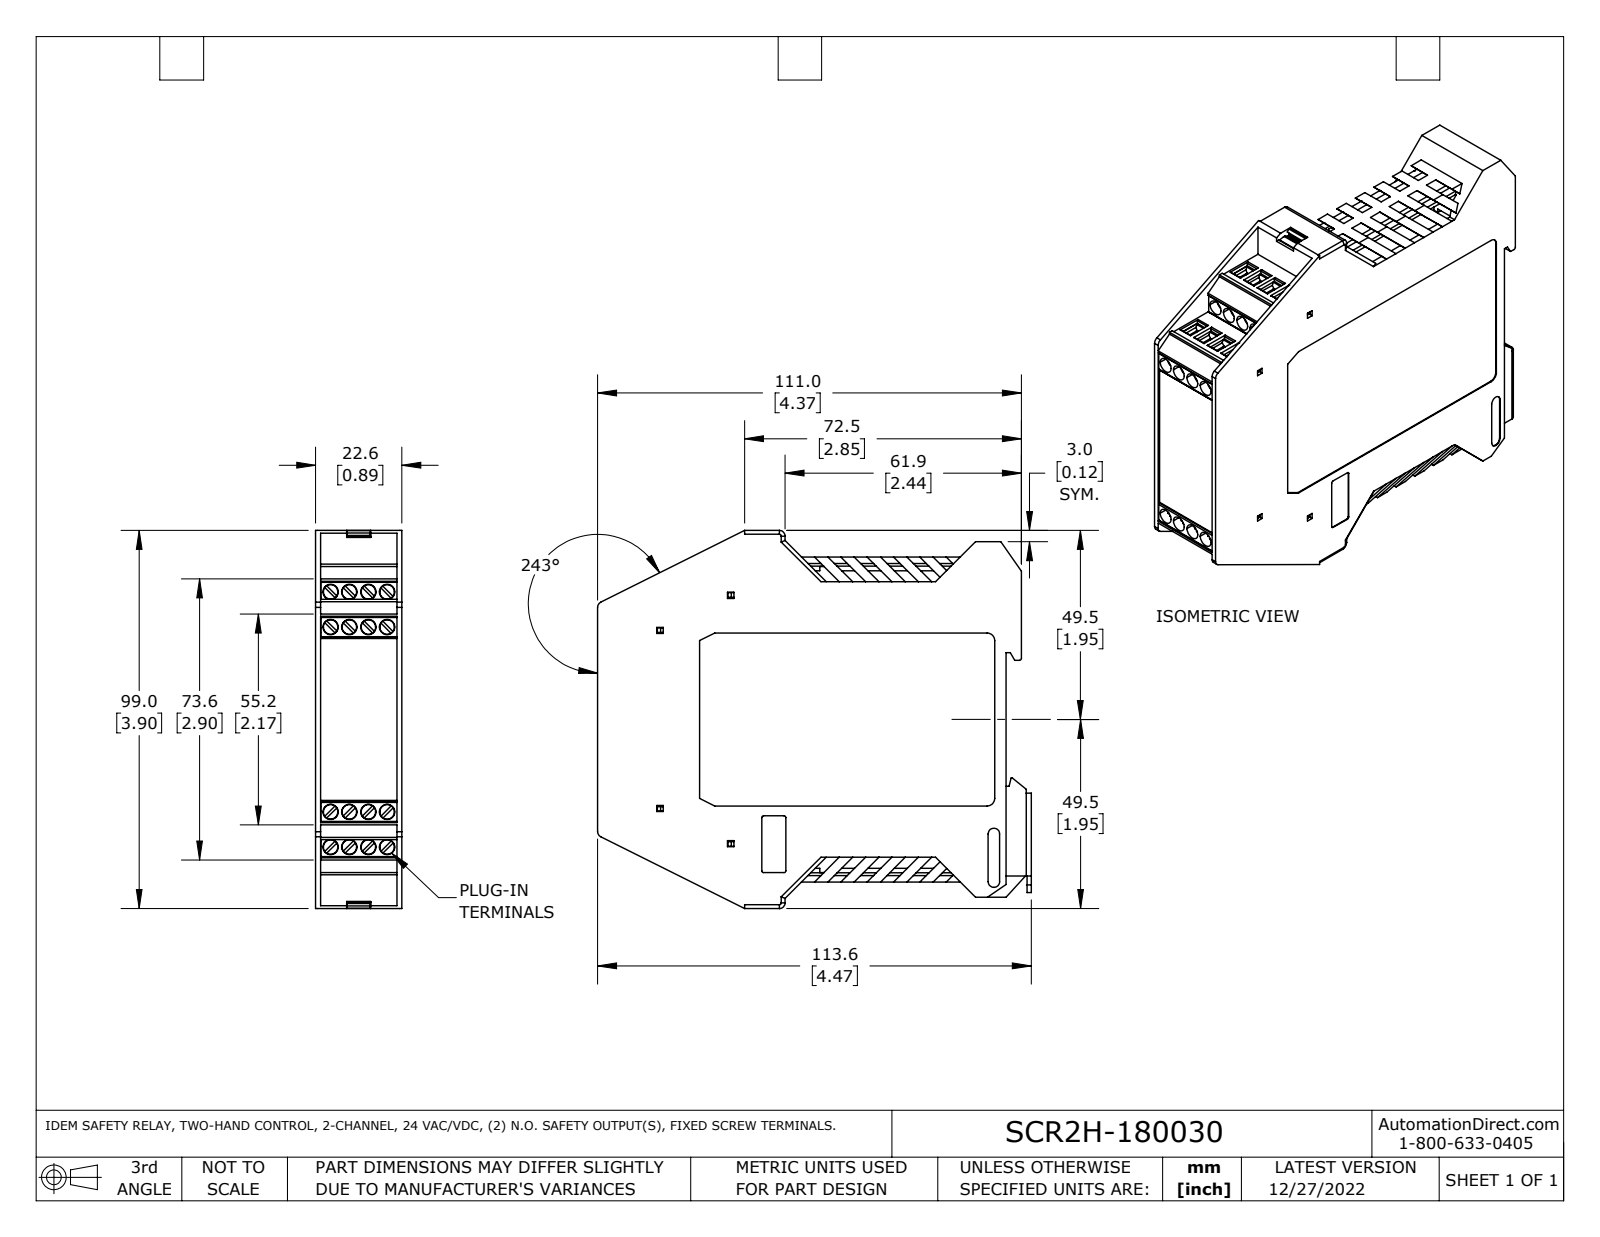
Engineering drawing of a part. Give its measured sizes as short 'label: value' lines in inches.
name: SCR2H-180030
written by: SolidWorks 2021 (AUTOMOTIVE_DESIGN)
unit: in
bodies: 6 solids, 1830 faces (1545 planar, 273 cylindrical, 12 other)
size: 4.472 × 3.898 × 0.89
volume: 3.923 in³; area: 100.6 in²
holes: 16× ⌀0.157, 2× ⌀0.079
bosses: 16× ⌀0.15, 16× ⌀0.055, 2× ⌀0.075
rounds: 39× R0.02, 24× R0.012, 18× R0.008, 6× R0.059, 4× R0.026, 4× R0.031, 4× R0.079, 2× R0.051
face distances: 0.831, 0.051, 0.059, 0.823, 0.882, 0.772, 0.89, 0.043, 0.78, 0.839
hole spacings: 0.193, 0.362, 0.39, 0.41, 0.532, 2.268, 2.276, 2.301
